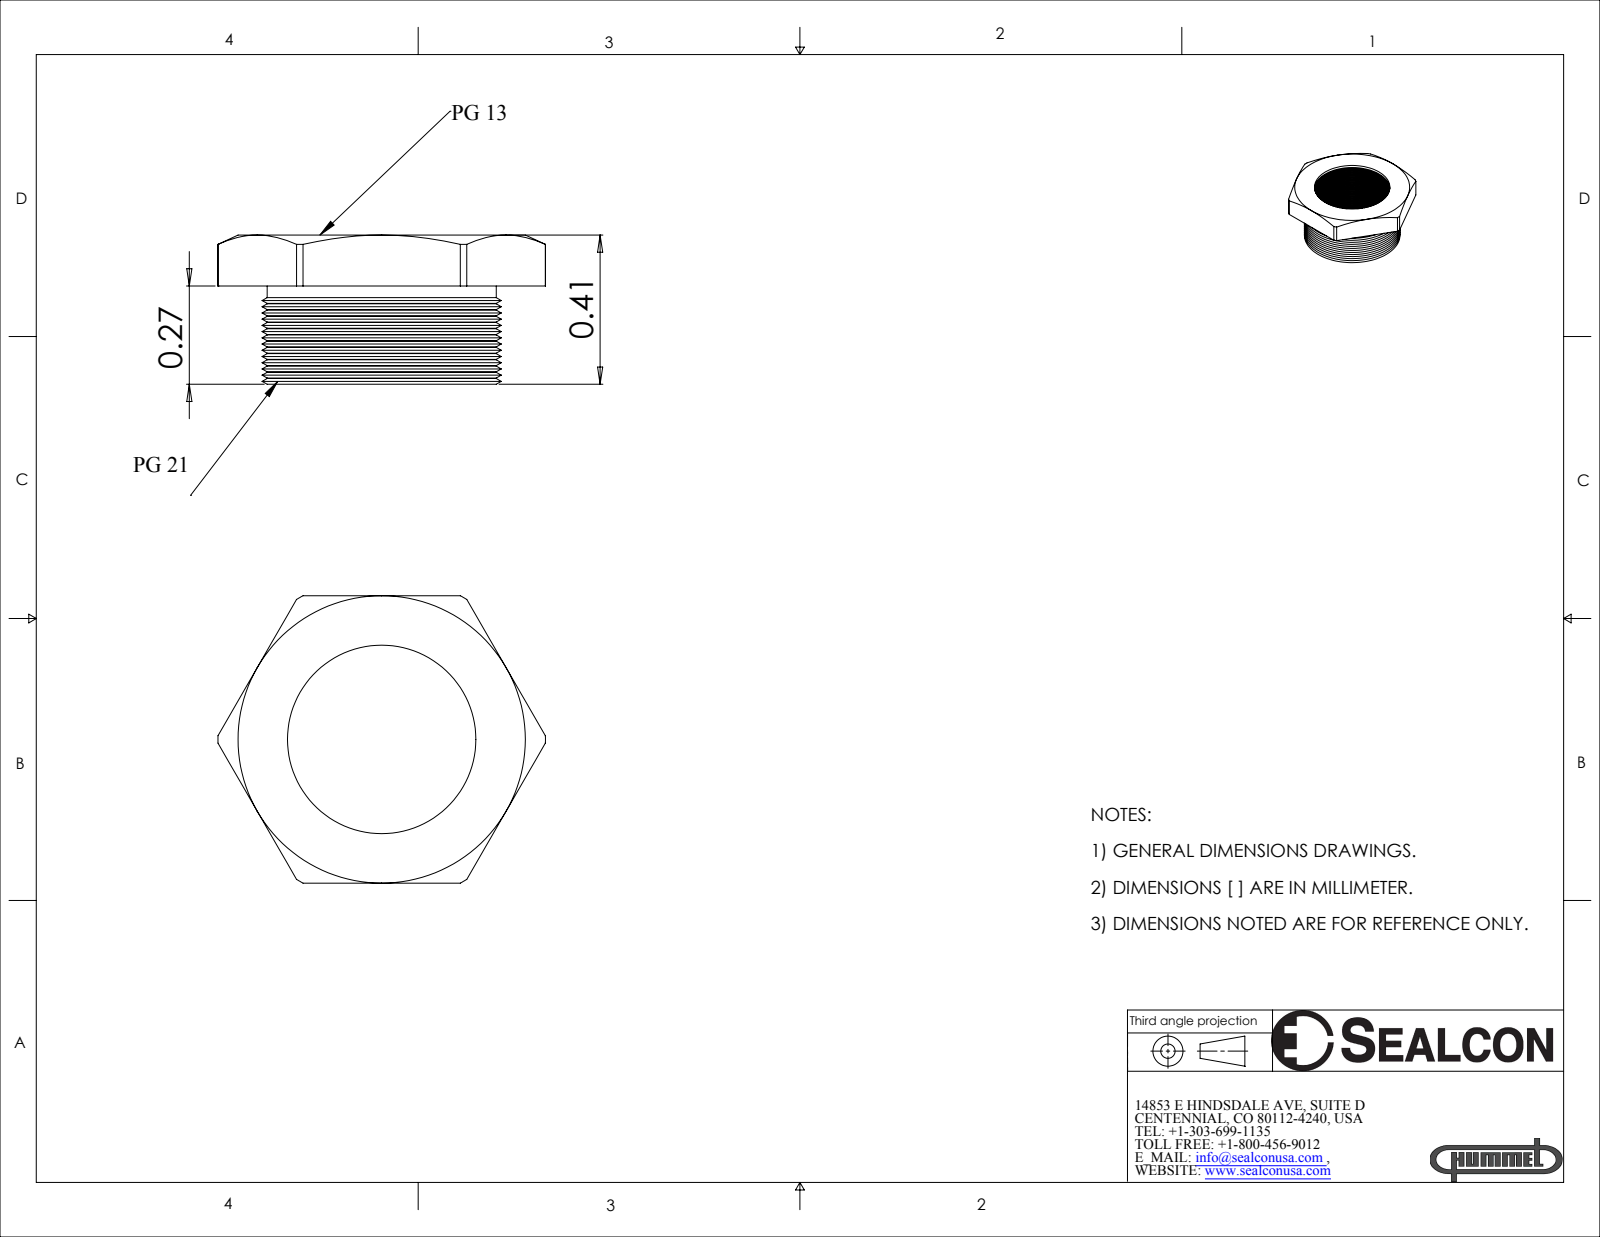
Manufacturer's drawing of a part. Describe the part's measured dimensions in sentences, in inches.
The part is named "RP-2113-BR". Its 3-D file was written by "SolidWorks 2008 (CONFIG_CONTROL_DESIGN)". It is 1 solid with 261 faces: 9 planar, 89 cylindrical and 163 other. Overall it measures 0.901 by 0.79 by 0.41 inches. Its volume is 0.074 cubic inches and its surface area 3.365 square inches. Round holes: 1 of diameter 0.518. Round bosses or shafts: 1 of diameter 0.63. Partial cylindrical surfaces (rounded edges, fillets, slot ends): 1 of radius 0.45. The main face-to-face distances are 0.14, 0.79, 0.27, 0.41.
